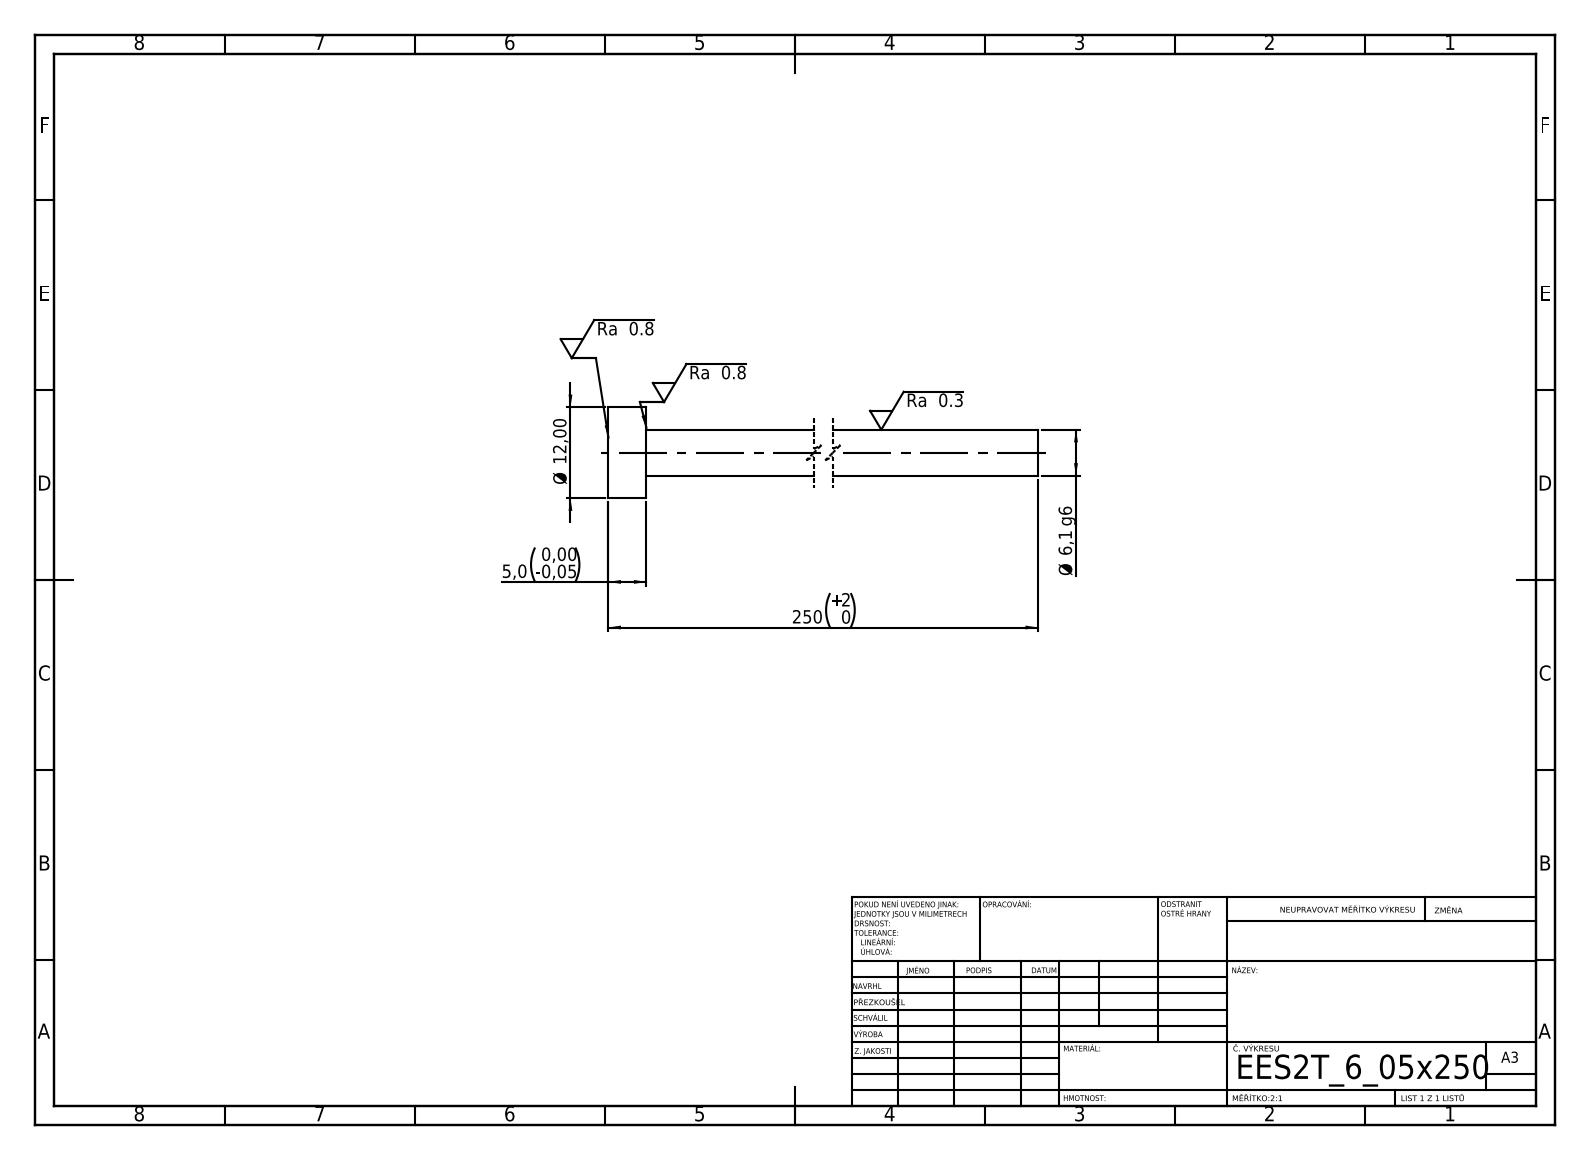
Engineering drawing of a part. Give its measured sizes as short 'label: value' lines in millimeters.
written by: SolidWorks 2019 (CONFIG_CONTROL_DESIGN)
unit: mm
bodies: 1 solid, 7 faces (3 planar, 4 cylindrical, 0 other)
size: 250 × 12 × 12
volume: 7 609 mm³; area: 5 071 mm²
bosses: 1× ⌀12, 1× ⌀6.05
face distances: 5, 250, 245
